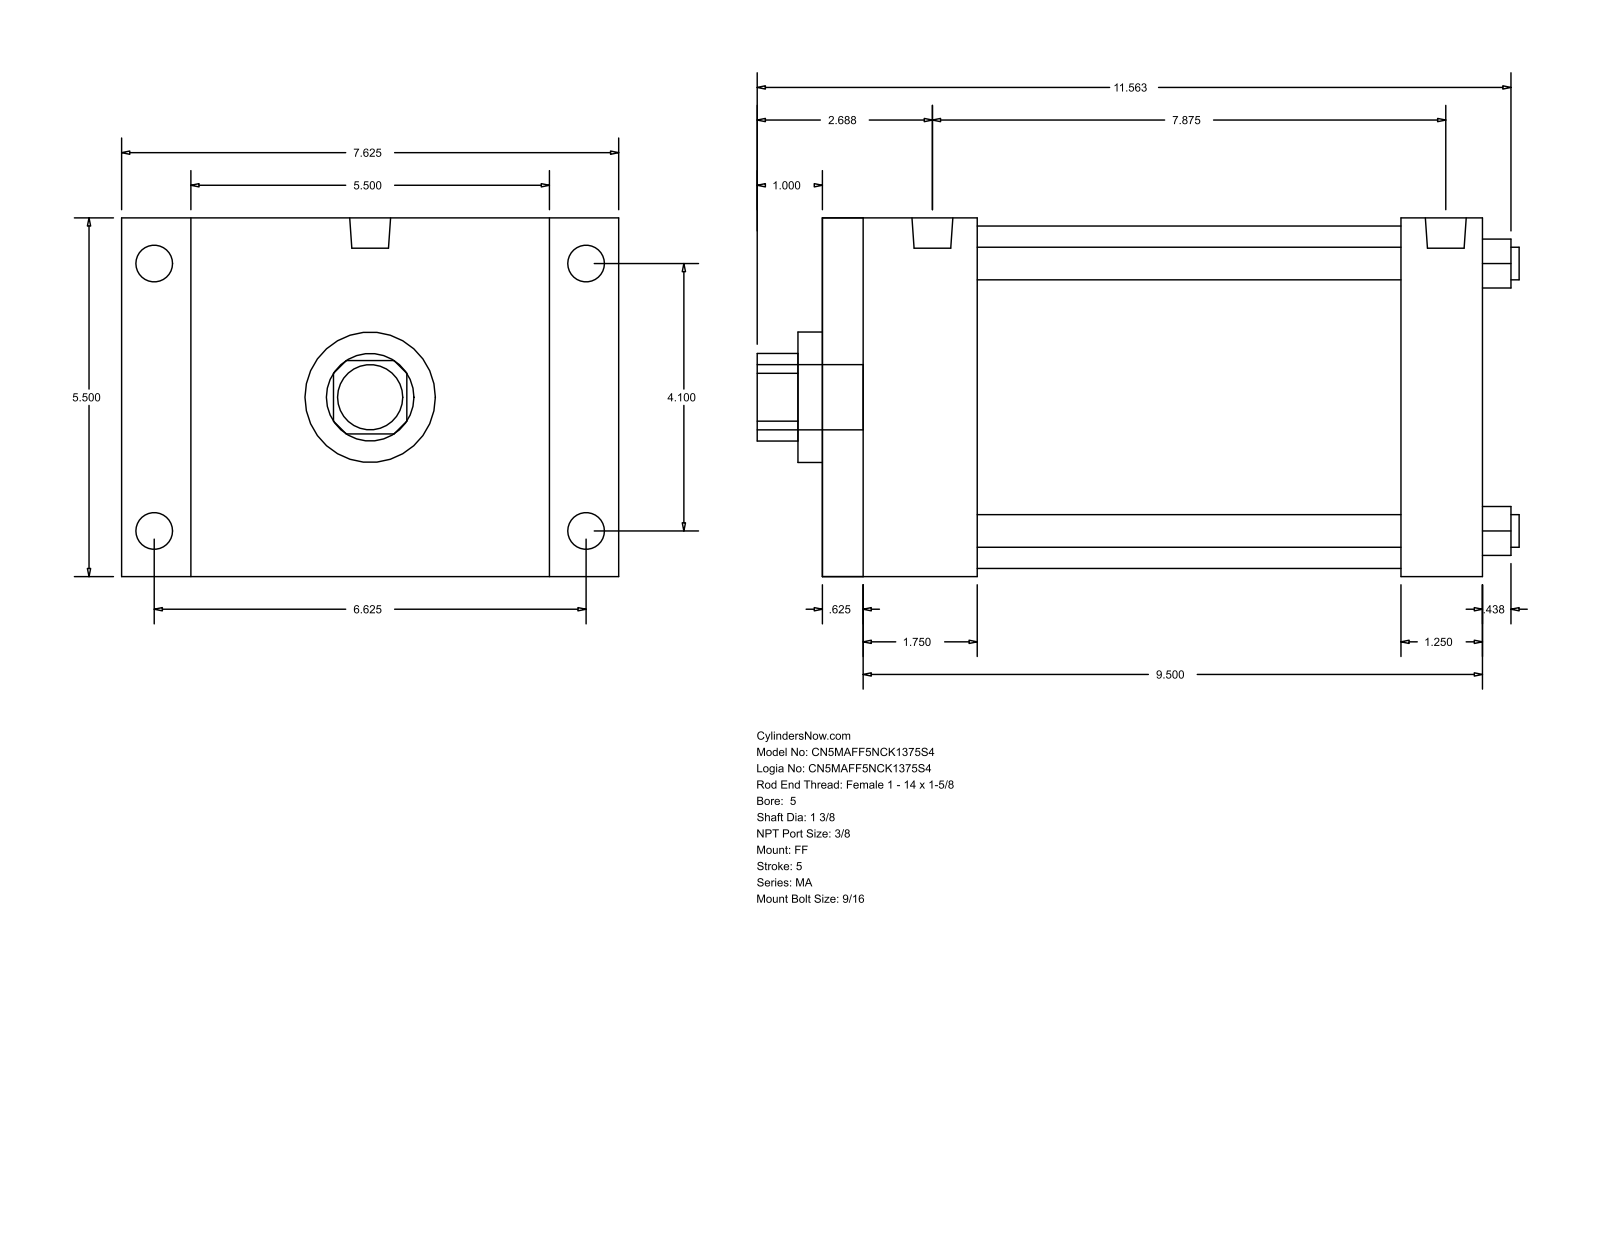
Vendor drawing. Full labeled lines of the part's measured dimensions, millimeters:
Part name (STEP PRODUCT): MA_FF__0500_1.375
STEP written by: GSSL Pune (CONFIG_CONTROL_DESIGN)
Units: millimetres
Bodies: 0 solids, 92 faces (64 planar, 28 cylindrical, 0 other)
Overall size (bounding box): 296.86 × 193.68 × 139.7
Round holes (diameter × count): ⌀12.7 ×4, ⌀34.92 ×1, ⌀50.8 ×1, ⌀133.35 ×1
Round bosses / shafts (diameter × count): ⌀14.29 ×4, ⌀11.11 ×4, ⌀15.93 ×2, ⌀25.4 ×1
Partial cylindrical surfaces — rounded edges, fillets, slot ends (radius × count): R17.06 ×1
Main face-to-face distances: 139.7, 257.17, 15.87, 241.3, 225.42, 209.55, 31.75, 60.32, 44.45, 165.1
Hole centre spacings: 73.64, 104.14, 147.28
